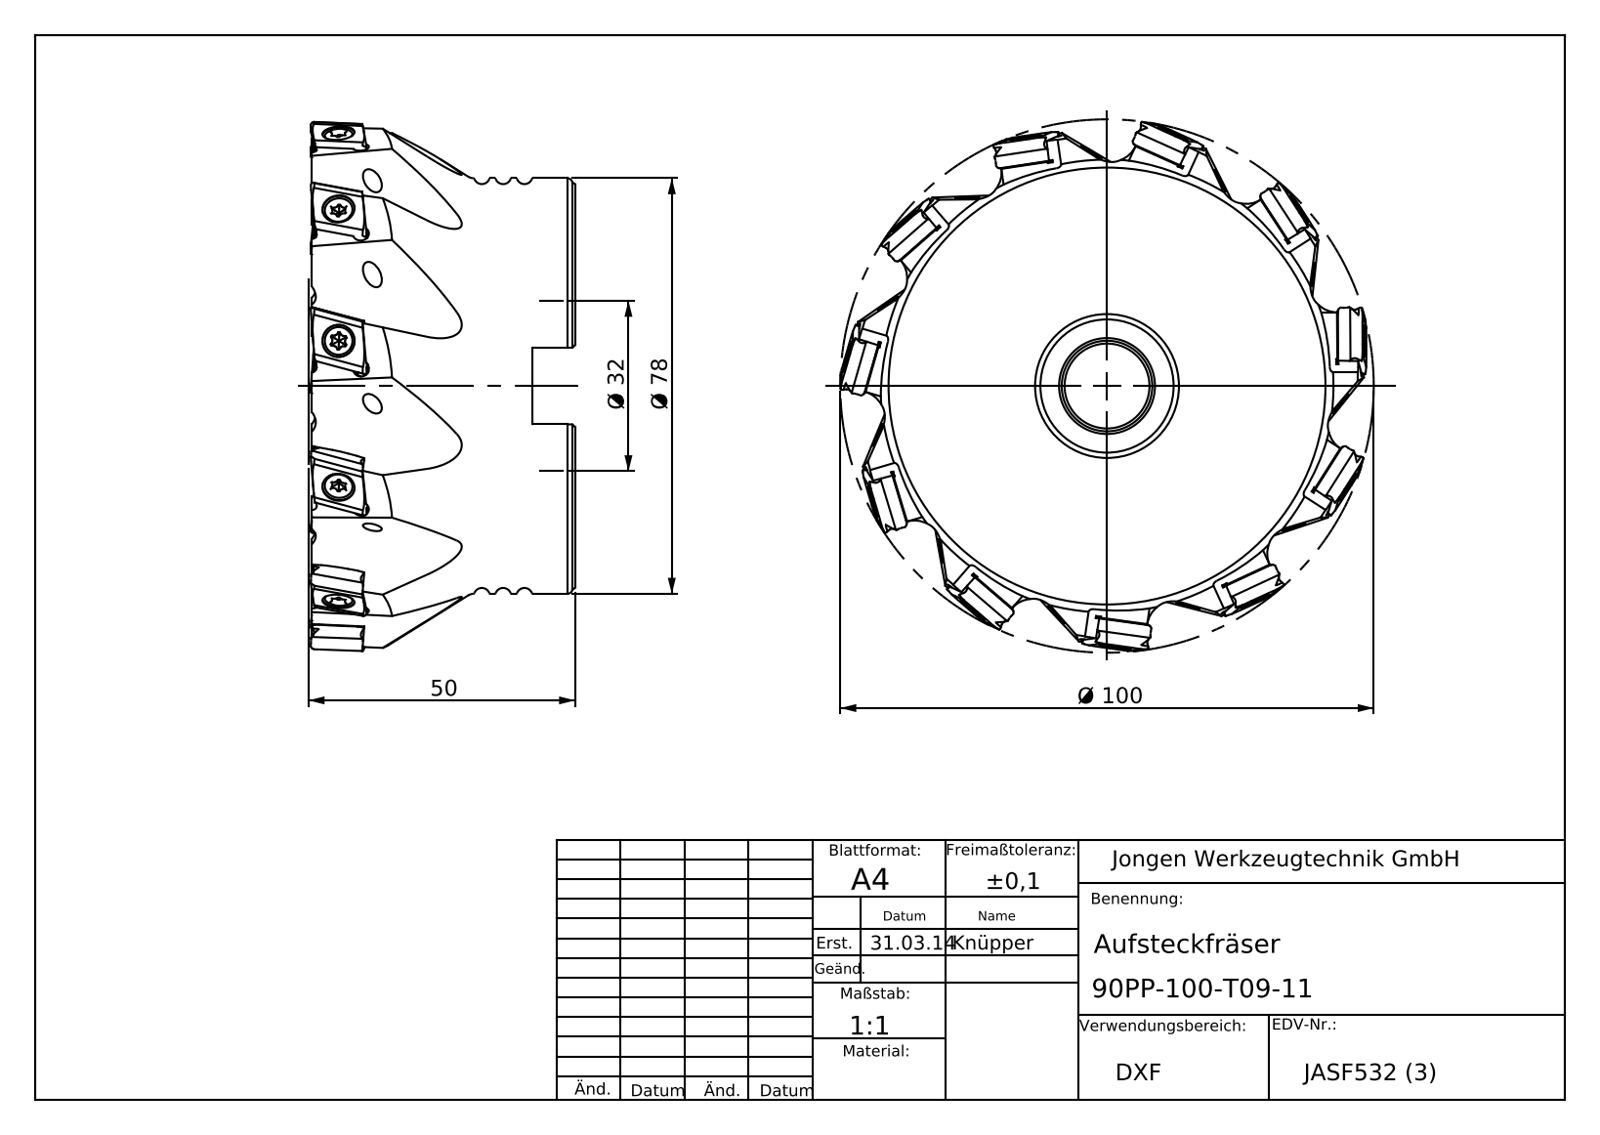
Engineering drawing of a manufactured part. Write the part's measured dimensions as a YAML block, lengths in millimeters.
part_name: "90PP_100_T09_11"
step_written_by: "SolidWorks 2015 (AUTOMOTIVE_DESIGN)"
units: millimeters
bodies: {solids: 1, faces: 326, planar: 132, cylindrical: 88, other: 106}
overall_size: [99.98, 99.98, 50.1]
volume: 238048
surface_area: 40607
round_holes:
  - {diameter: 3, count: 13}
  - {diameter: 3.3, count: 13}
  - {diameter: 17, count: 1}
  - {diameter: 25, count: 1}
  - {diameter: 32, count: 1}
  - {diameter: 32.15, count: 1}
  - {diameter: 32.3, count: 1}
round_bosses_or_shafts:
  - {diameter: 99.98, count: 1}
  - {diameter: 78, count: 1}
partial_cylinders:
  - {radius: 0.9, count: 13}
  - {radius: 1.5, count: 13}
  - {radius: 3, count: 13}
face_to_face_distances: [46.9, 8, 38.9, 25, 17, 21.9, 14.4, 30.9, 22.9, 5.9]
